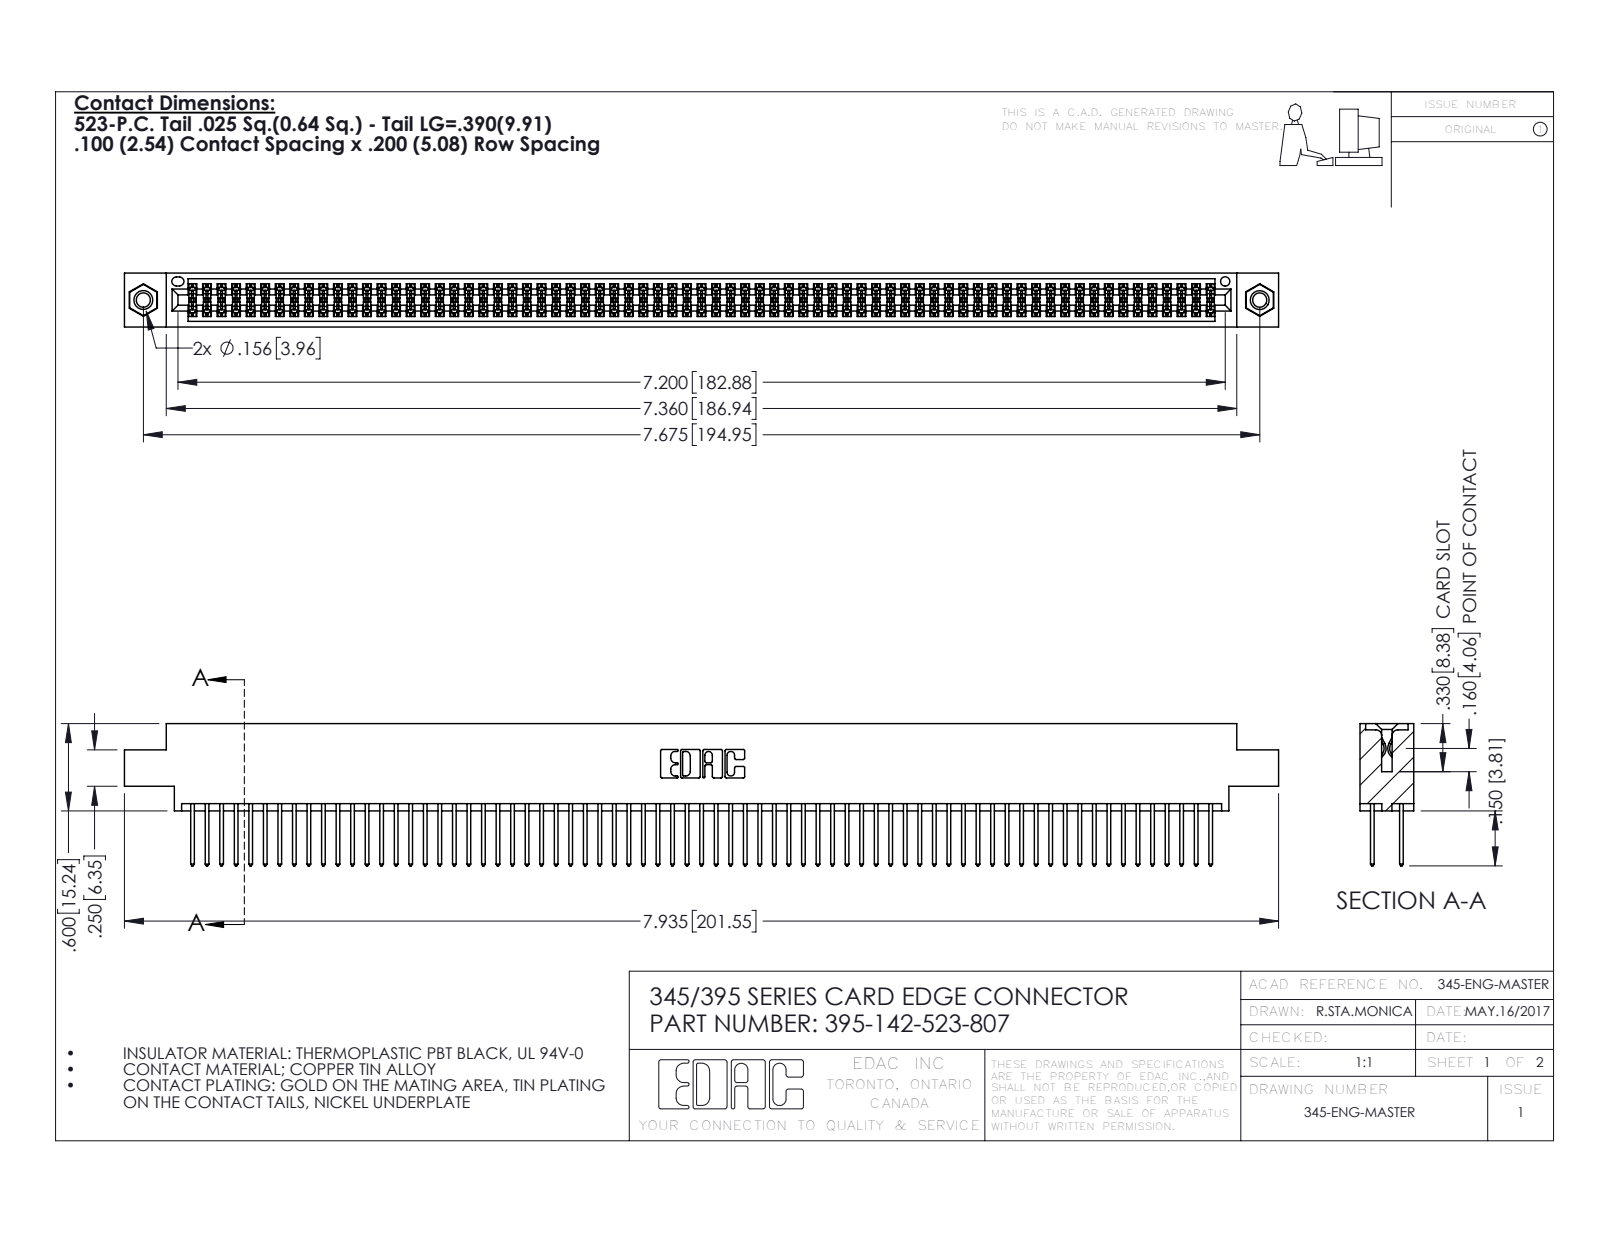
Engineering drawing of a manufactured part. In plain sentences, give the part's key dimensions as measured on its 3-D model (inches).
The part is named "395-142-523-807; 345-292-001_345-293-123; 345-250-001_345-250-005-103; 345 Part_0.170 Offset - 0.156 Dia-TI". Its 3-D file was written by "SolidWorks 2016 (CONFIG_CONTROL_DESIGN)". It is 145 solids with 7290 faces: 4802 planar, 2472 cylindrical and 16 other. Overall it measures 7.935 by 0.977 by 0.37 inches. Its volume is 1.221 cubic inches and its surface area 49.01 square inches. Round holes: 2 of diameter 0.098, 2 of diameter 0.125, 2 of diameter 0.156, 1 of diameter 0.064. Round bosses or shafts: 2 of diameter 0.155. Partial cylindrical surfaces (rounded edges, fillets, slot ends): 213 of radius 0.006, 142 of radius 0.01, 22 of radius 0.01, 6 of radius 0.007, 6 of radius 0.031, 3 of radius 0.026, 2 of radius 0.014, 2 of radius 0.019. The main face-to-face distances are 0.072, 0.298, 0.2, 0.098, 0.272, 0.025, 0.37, 0.225, 0.175, 0.149. The hole center spacings are 0.27, 7.439, 7.675.
